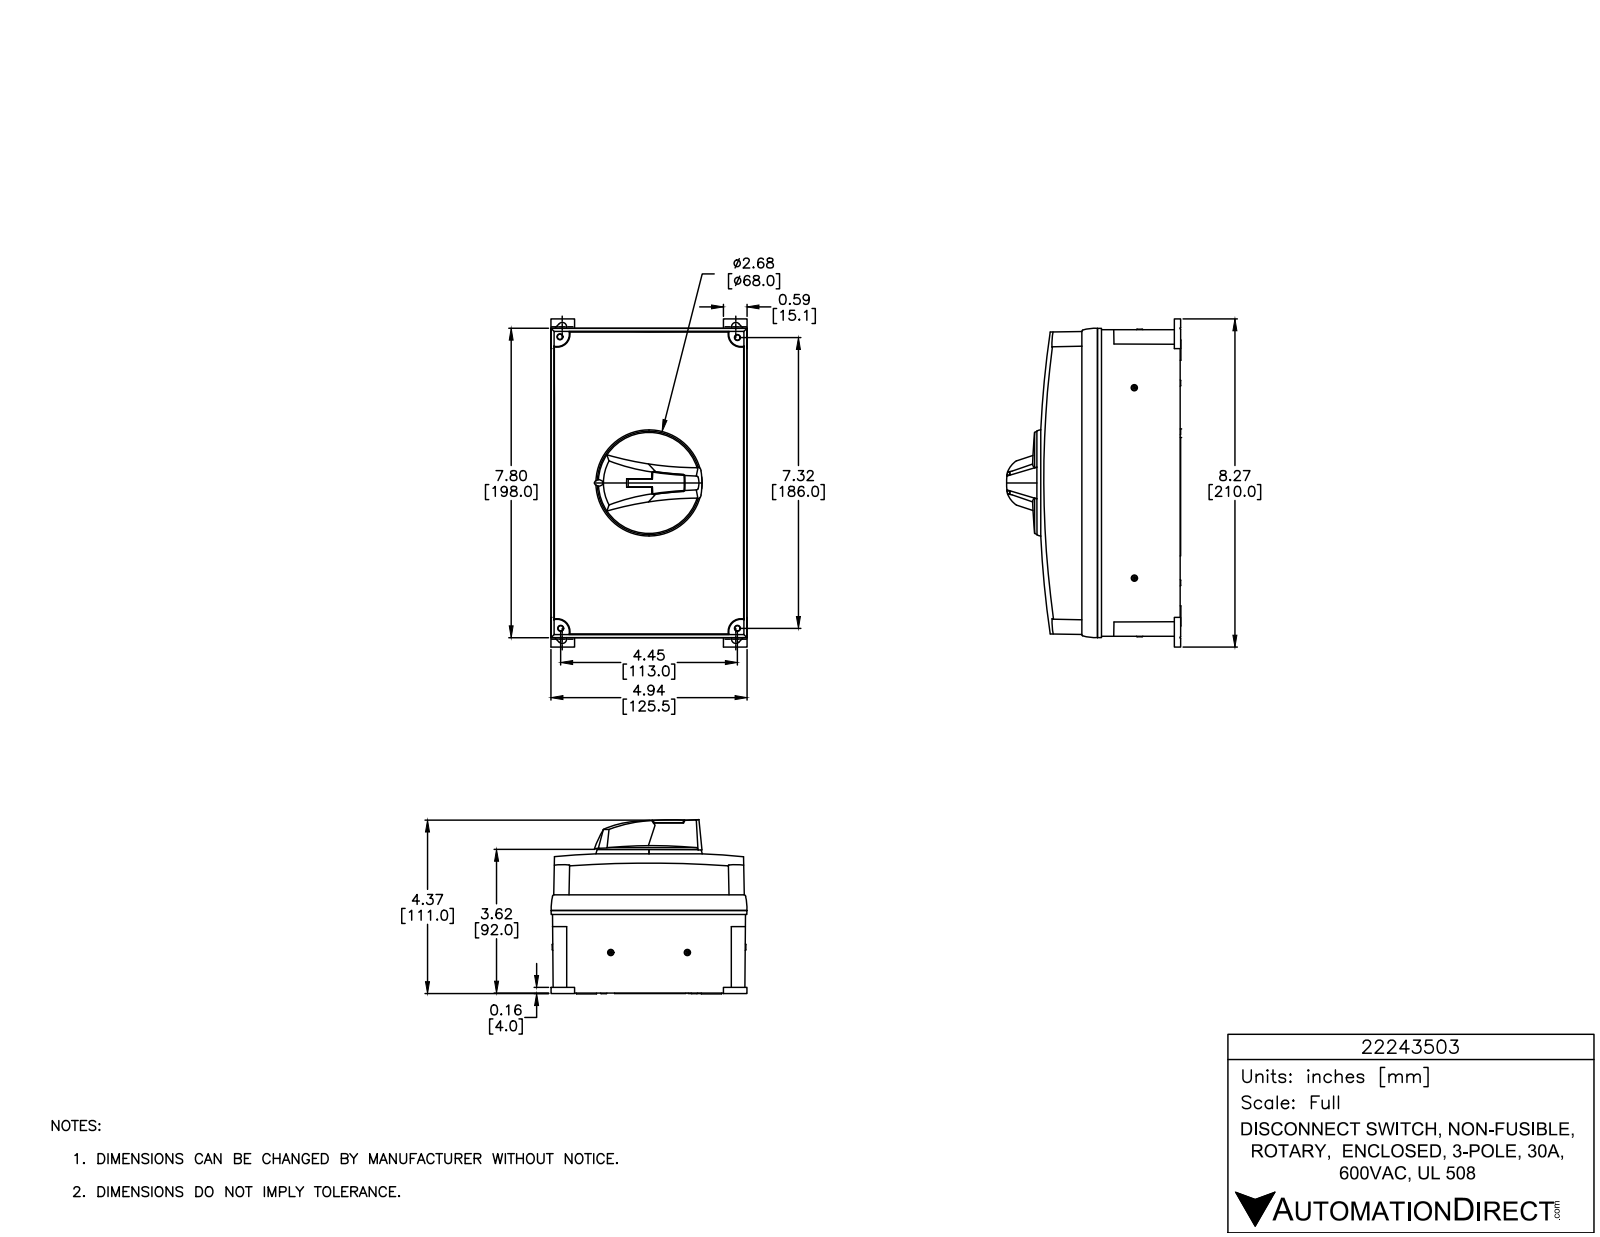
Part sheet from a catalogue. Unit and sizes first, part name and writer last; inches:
Units: inches
Overall size (bounding box): 8.26 × 4.934 × 4.394
Round holes (diameter × count): ⌀0.26 ×6, ⌀0.134 ×4, ⌀0.15 ×4, ⌀0.339 ×1, ⌀2.474 ×1
Round bosses / shafts (diameter × count): ⌀0.236 ×8, ⌀0.508 ×4, ⌀0.394 ×2, ⌀0.272 ×2, ⌀2.772 ×1, ⌀1.244 ×1, ⌀0.371 ×1, ⌀0.173 ×1
Partial cylindrical surfaces — rounded edges, fillets, slot ends (radius × count): R0.006 ×64, R0.108 ×8, R0.02 ×3, R0.107 ×2, R0.276 ×2, R0.835 ×2, R0.012 ×1, R0.033 ×1
Main face-to-face distances: 0.118, 0.119, 3.107, 2.083, 1.965, 7.72, 0.665, 1.098, 1.024, 2.989
Hole centre spacings: 0.689, 2.325, 2.22, 4.324, 1.11, 1.304, 1.309, 1.378
Volume: 35.21 in³ · Surface area: 425.4 in²
Bodies: 7 solids, 3465 faces (2977 planar, 242 cylindrical, 246 other)
Part name (STEP PRODUCT): 22243503
STEP written by: SolidWorks 2015 (AUTOMOTIVE_DESIGN)
